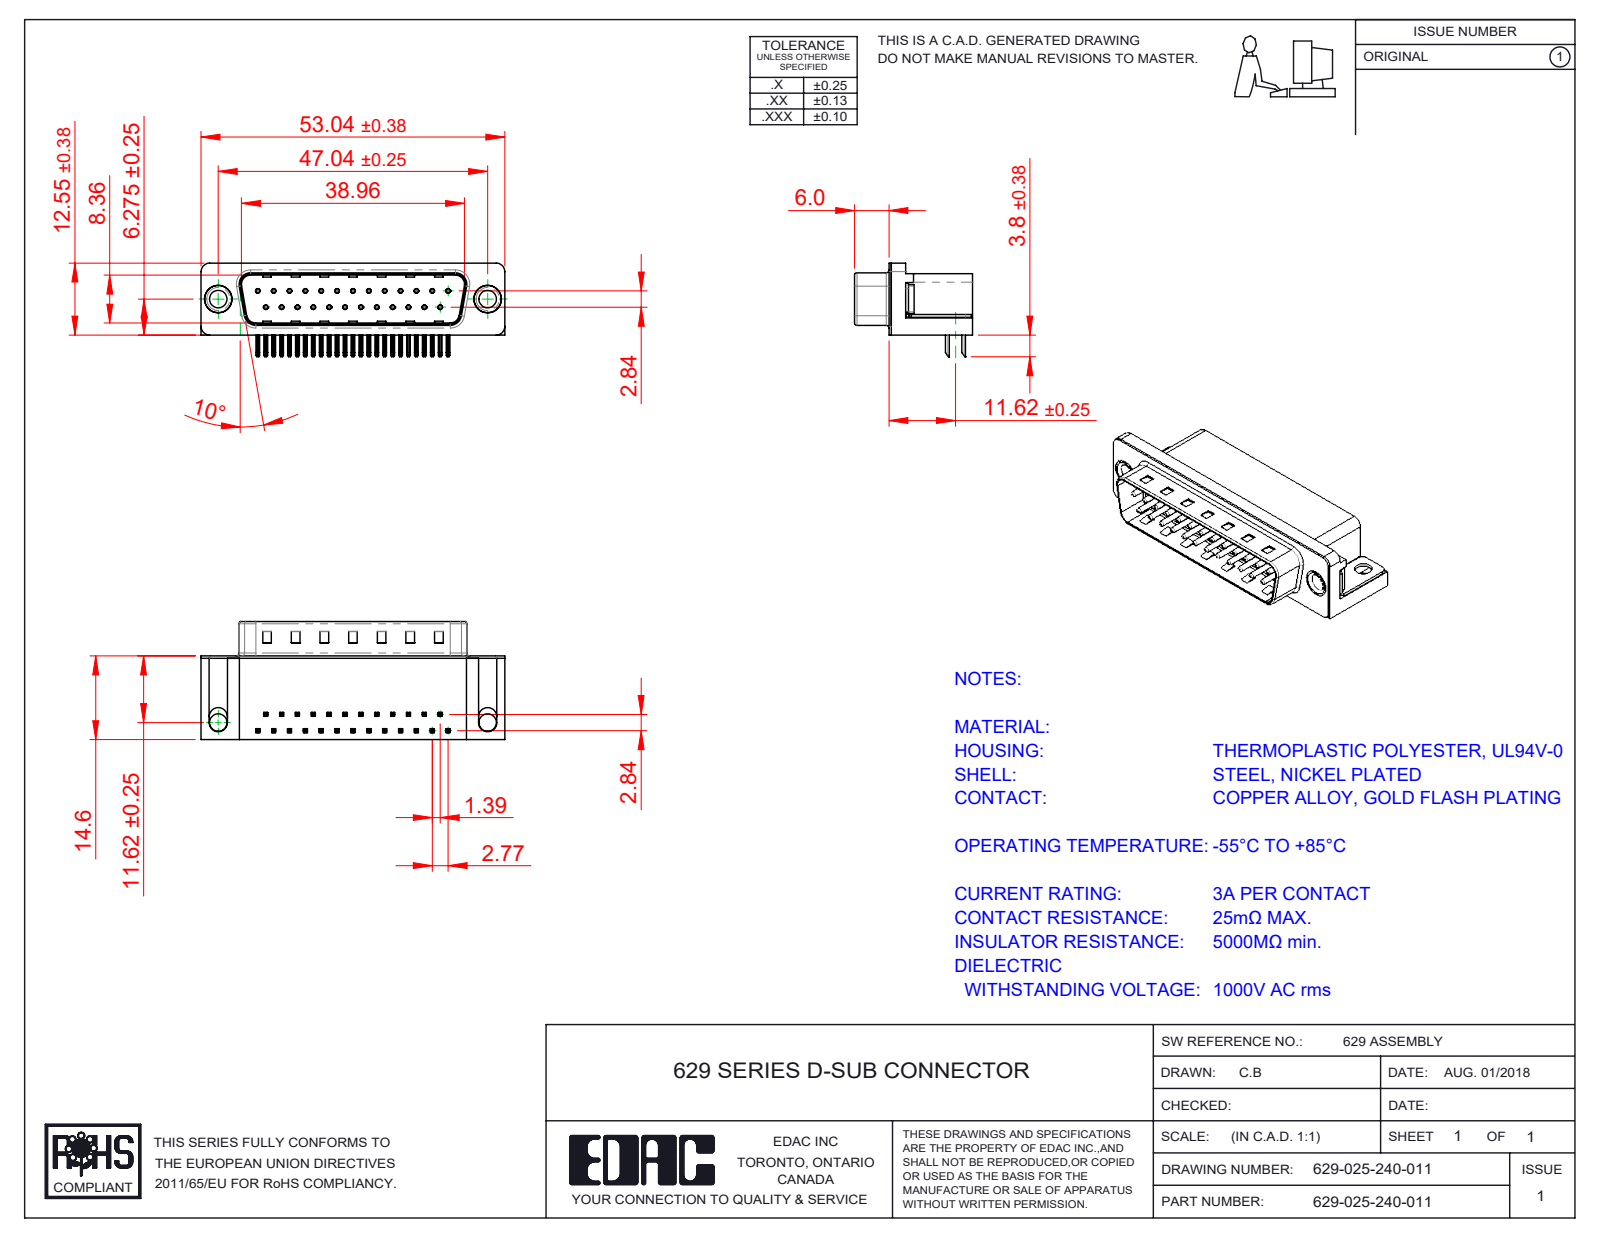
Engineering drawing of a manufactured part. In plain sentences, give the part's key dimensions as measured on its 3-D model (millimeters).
The part is named "629 Housing_25 Socket; 629 Contact Top; 629-025-240-011; 629 Shell_25 Socket (+3 more)". Its 3-D file was written by "SolidWorks 2020 (CONFIG_CONTROL_DESIGN)". It is 31 solids with 2221 faces: 1403 planar, 641 cylindrical and 177 other. Overall it measures 53.04 by 20.6 by 16.35 millimeters. Its volume is 7 310 cubic millimeters and its surface area 8 191 square millimeters. Round holes: 25 of diameter 0.35, 25 of diameter 0.8, 4 of diameter 3.05, 2 of diameter 4, 2 of diameter 4.8, 2 of diameter 5. Round bosses or shafts: 25 of diameter 0.75, 2 of diameter 4.9, 2 of diameter 4.75, 2 of diameter 3.85. Partial cylindrical surfaces (rounded edges, fillets, slot ends): 108 of radius 0.25, 50 of radius 0.12, 16 of radius 1, 9 of radius 0.5, 8 of radius 1.6, 7 of radius 1.5, 4 of radius 0.9, 4 of radius 2. The main face-to-face distances are 0.4, 10.36, 14.2, 2.1, 8.76, 1.7, 10.46, 10.86, 14.6, 2.9. The hole center spacings are 3.16, 2.77, 5.54, 8.31, 11.08, 13.85, 16.62, 5.03.
